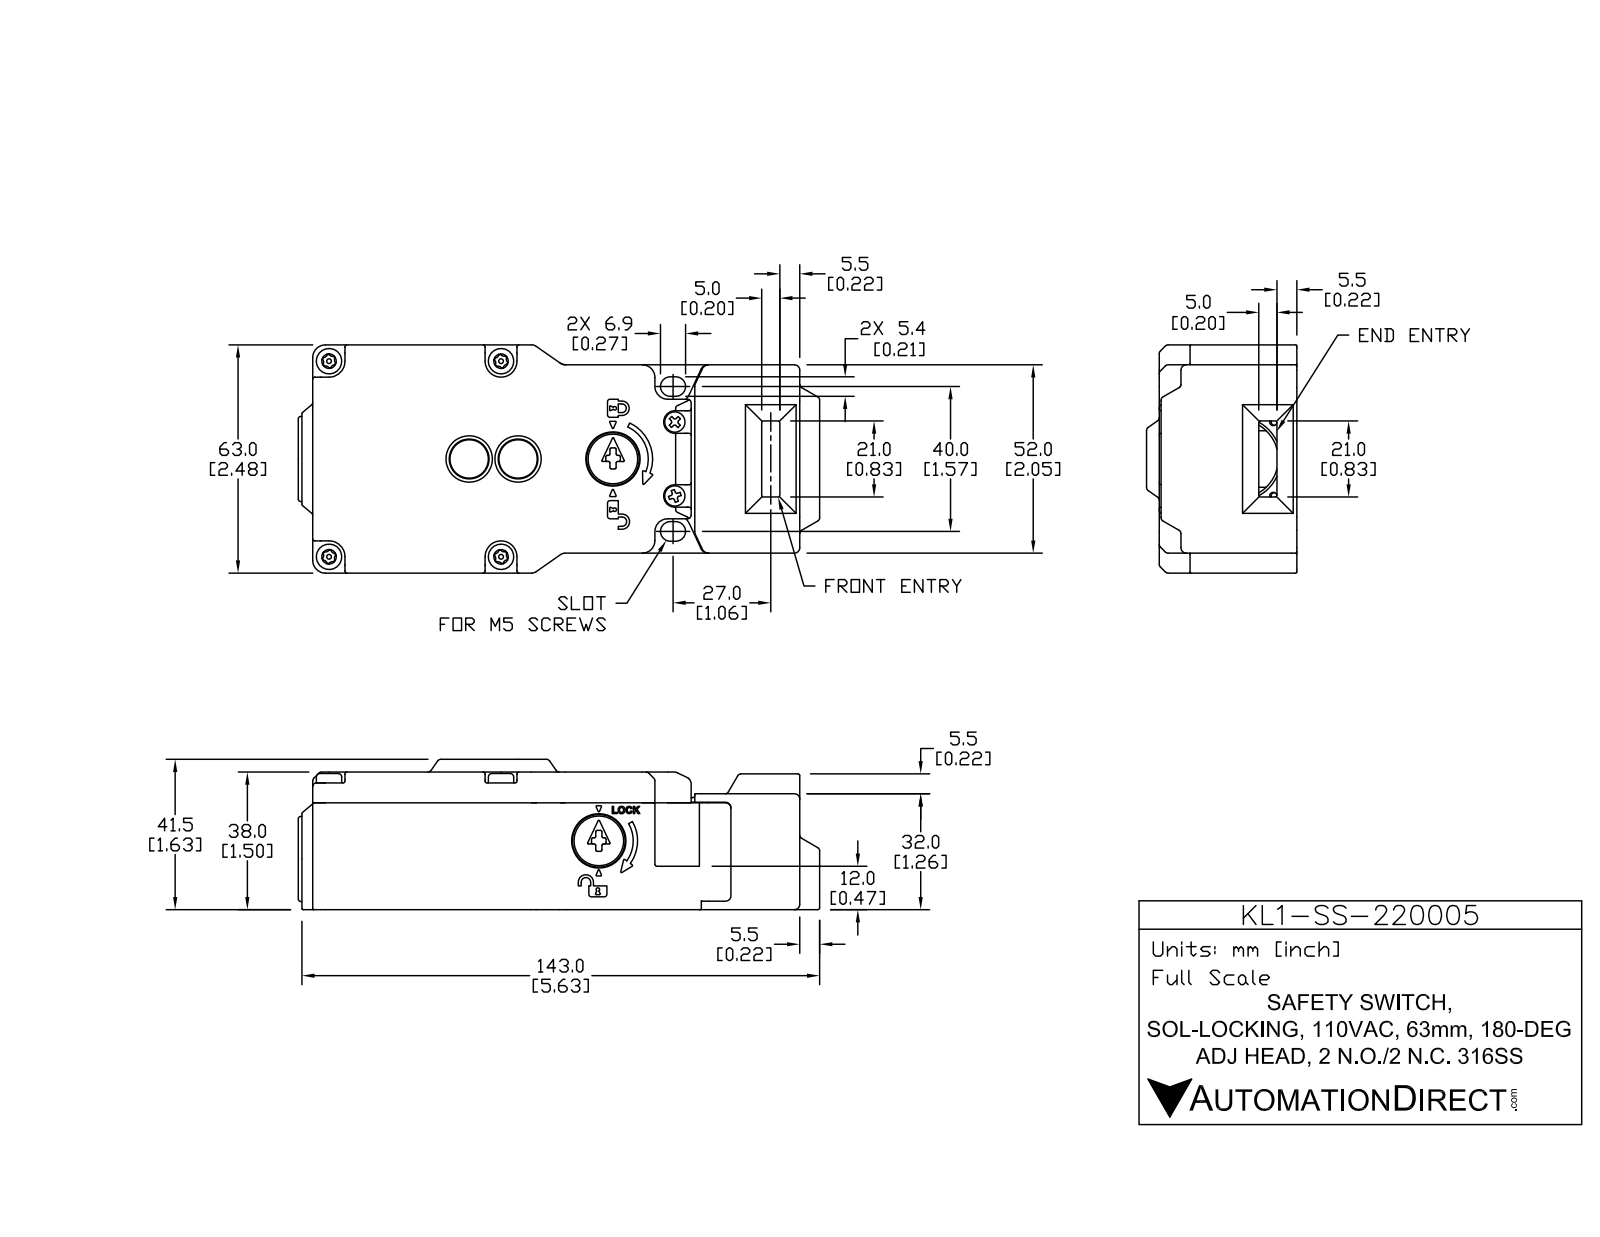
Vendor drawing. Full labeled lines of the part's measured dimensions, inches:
Part name (STEP PRODUCT): KL1-SS-220005
STEP written by: SolidWorks 2017 (AUTOMOTIVE_DESIGN)
Units: inches
Bodies: 18 solids, 3047 faces (909 planar, 1225 cylindrical, 913 other)
Overall size (bounding box): 5.669 × 2.48 × 1.634
Volume: 6.348 in³ · Surface area: 118.8 in²
Round holes (diameter × count): ⌀0.102 ×4, ⌀0.134 ×4, ⌀0.157 ×4, ⌀0.161 ×4, ⌀0.177 ×4, ⌀0.197 ×4, ⌀0.079 ×2, ⌀0.083 ×2, ⌀0.118 ×2, ⌀0.126 ×2, ⌀0.142 ×2, ⌀0.264 ×2
Round bosses / shafts (diameter × count): ⌀0.276 ×4, ⌀0.138 ×4, ⌀0.051 ×4, ⌀0.197 ×3, ⌀0.039 ×3, ⌀0.571 ×2, ⌀0.417 ×2, ⌀0.362 ×2
Partial cylindrical surfaces — rounded edges, fillets, slot ends (radius × count): R0.02 ×348, R0.012 ×126, R0.039 ×106, R0.008 ×30, R0.016 ×24, R0.059 ×16, R0.006 ×14, R0.028 ×12
Main face-to-face distances: 0.098, 0.118, 0.217, 1.496, 1.398, 1.402, 1.303, 0.094, 2.264, 2.146
Hole centre spacings: 0.404, 0.498, 0.515, 0.549, 0.784, 0.803, 1.079, 1.118
